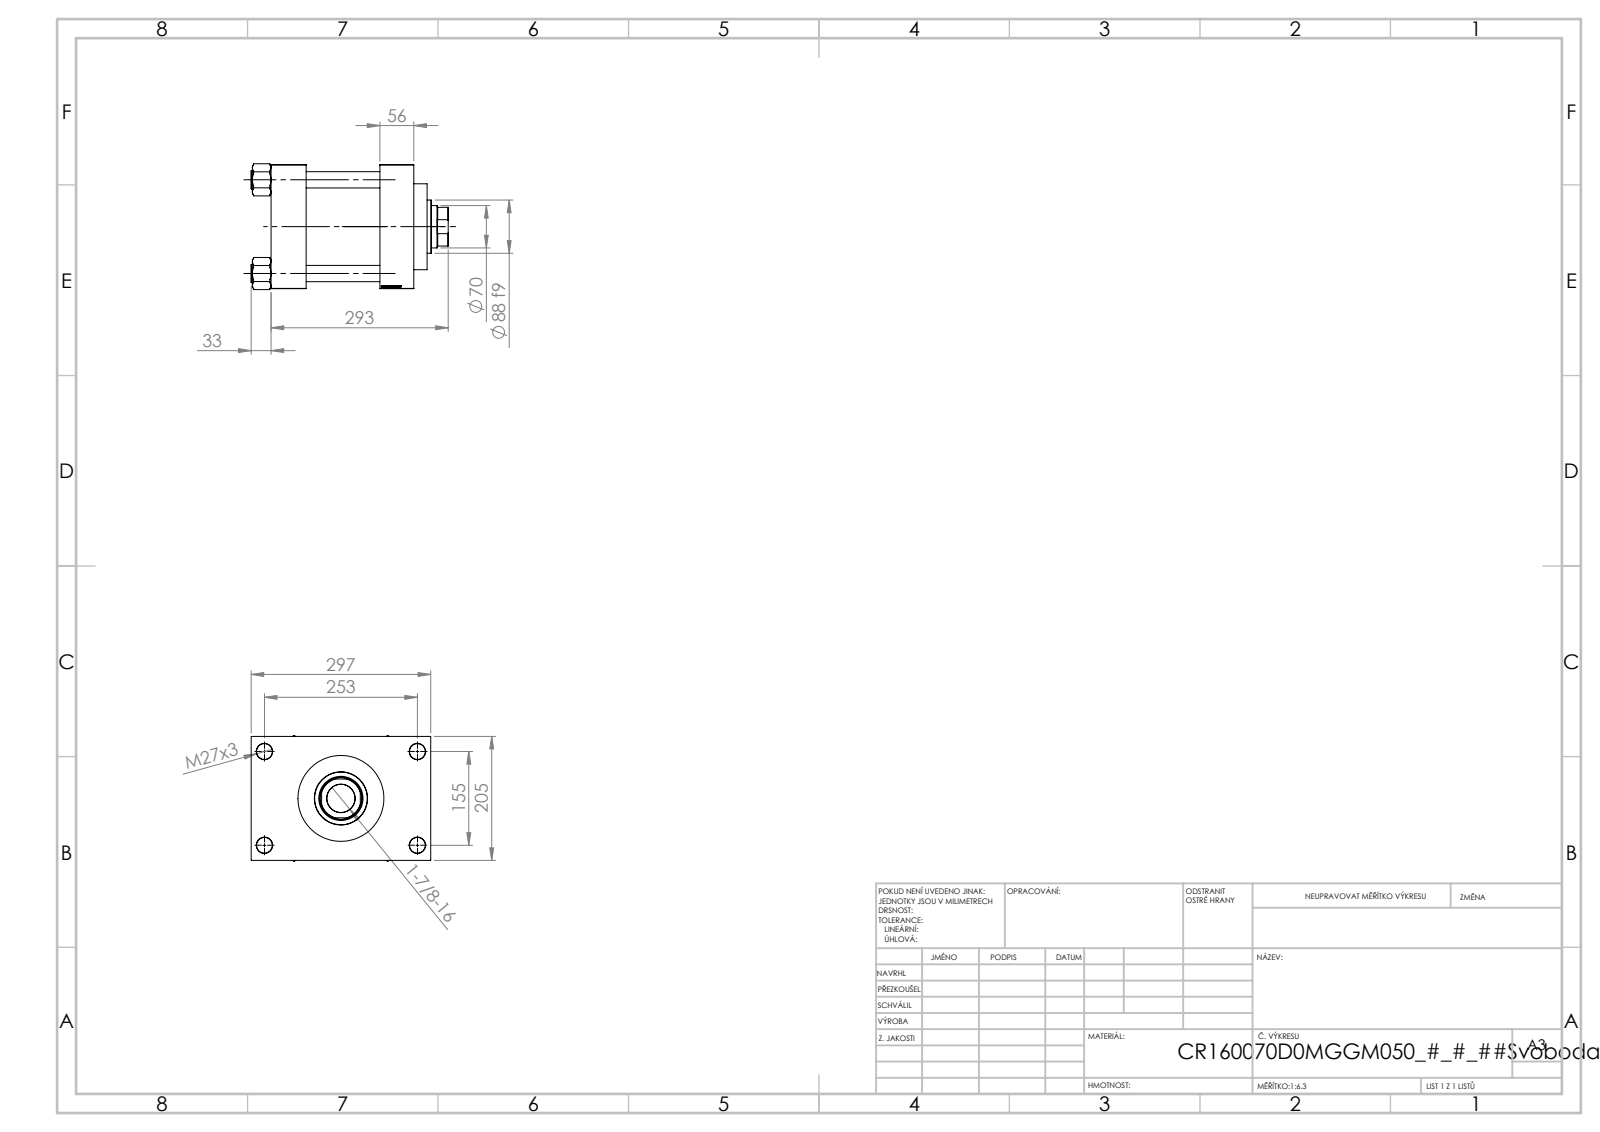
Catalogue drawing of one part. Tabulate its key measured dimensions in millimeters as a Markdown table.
| quantity | value |
| --- | --- |
| part name | NUT_M5_D; V215CR_D_Body; V215CR_D_TYCINKA; V215_VC_A (+1 more) |
| STEP written by | SolidWorks 2019 (CONFIG_CONTROL_DESIGN) |
| units | millimeters |
| bodies | 11 solids, 1149 faces (544 planar, 87 cylindrical, 518 other) |
| overall size | 326 × 297 × 208.14 |
| volume | 8 126 000 mm³ |
| surface area | 772 474 mm² |
| round holes (diameter × count) | 26 × 4, 27 × 4, 7 × 2, 33.24 × 2, 45 × 2, 46.5 × 1, 70 × 1, 73 × 1, 120 × 1, 142 × 1, 160 × 1 |
| round bosses / shafts (diameter × count) | 30 × 4, 166 × 1, 88 × 1 |
| partial cylindrical surfaces (radius × count) | 34 × 1 |
| main face-to-face distances | 58, 180, 122, 236, 178, 56, 205, 46, 251, 72 |
| hole center spacings | 49.05, 109.53, 148.35, 154.9, 162.53, 203.95, 256.13, 155 |
